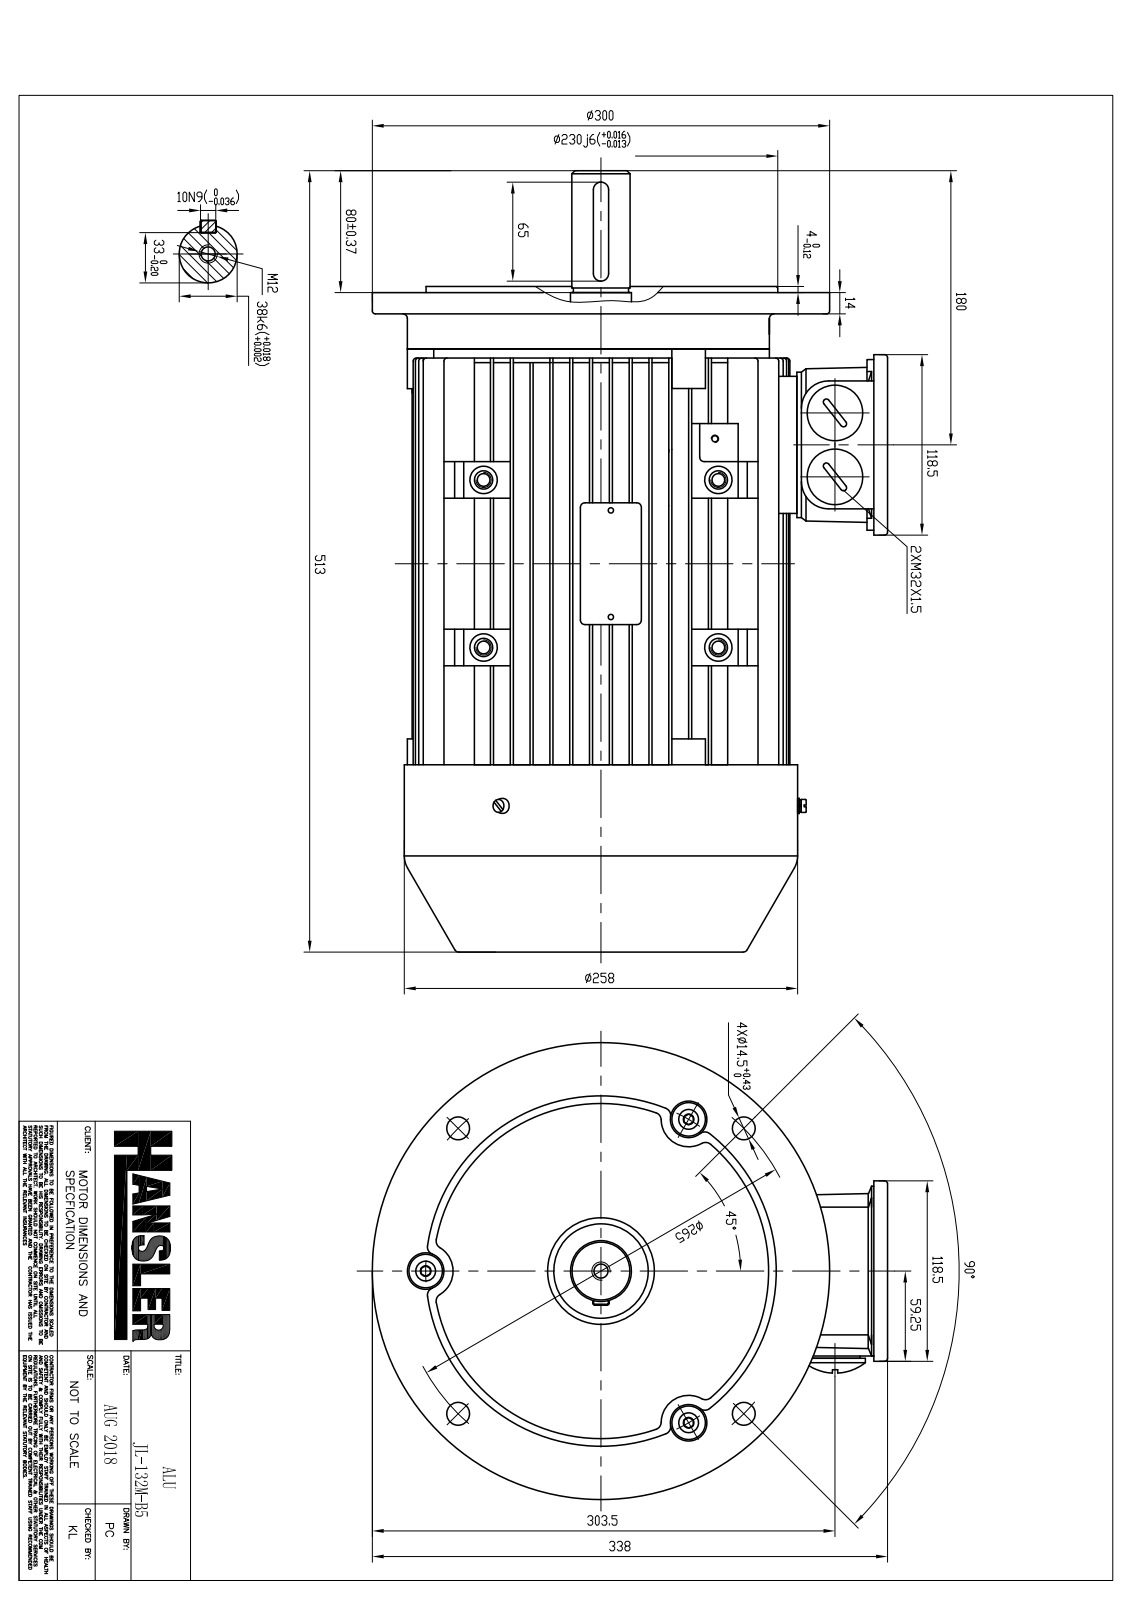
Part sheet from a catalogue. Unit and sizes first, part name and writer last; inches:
Units: inches
Overall size (bounding box): 20.197 × 13.425 × 11.811
Round holes (diameter × count): ⌀0.197 ×26, ⌀0.394 ×14, ⌀0.228 ×10, ⌀0.709 ×8, ⌀0.189 ×4, ⌀0.207 ×4, ⌀0.209 ×4, ⌀0.315 ×4, ⌀0.591 ×4, ⌀0.33 ×3, ⌀0.358 ×3, ⌀0.63 ×3
Round bosses / shafts (diameter × count): ⌀0.472 ×8, ⌀0.176 ×8, ⌀0.189 ×6, ⌀0.63 ×4, ⌀0.394 ×4, ⌀0.309 ×4, ⌀0.512 ×3, ⌀0.496 ×3
Partial cylindrical surfaces — rounded edges, fillets, slot ends (radius × count): R0.02 ×816, R0.079 ×46, R0.197 ×45, R0.118 ×32, R0.039 ×26, R0.157 ×26, R0.098 ×18, R0.236 ×12
Main face-to-face distances: 0.512, 0.079, 1.024, 0.433, 3.583, 4.094, 0.591, 3.071, 1.535, 0.945
Hole centre spacings: 1.584, 2.268, 2.406, 3.096, 3.32, 2.242, 5.698, 0.696
Volume: 231.7 in³ · Surface area: 2 881 in²
Bodies: 47 solids, 4970 faces (2942 planar, 1629 cylindrical, 399 other)
Part name (STEP PRODUCT): JL-132M-B5
STEP written by: SIEMENS PLM Software NX 12.0 (AP203_CONFIGURATION_CONTROLLED_3D_DESIGN_OF_MECHANICAL_PARTS_AND_ASSEMBLIES_MIM_LF)
